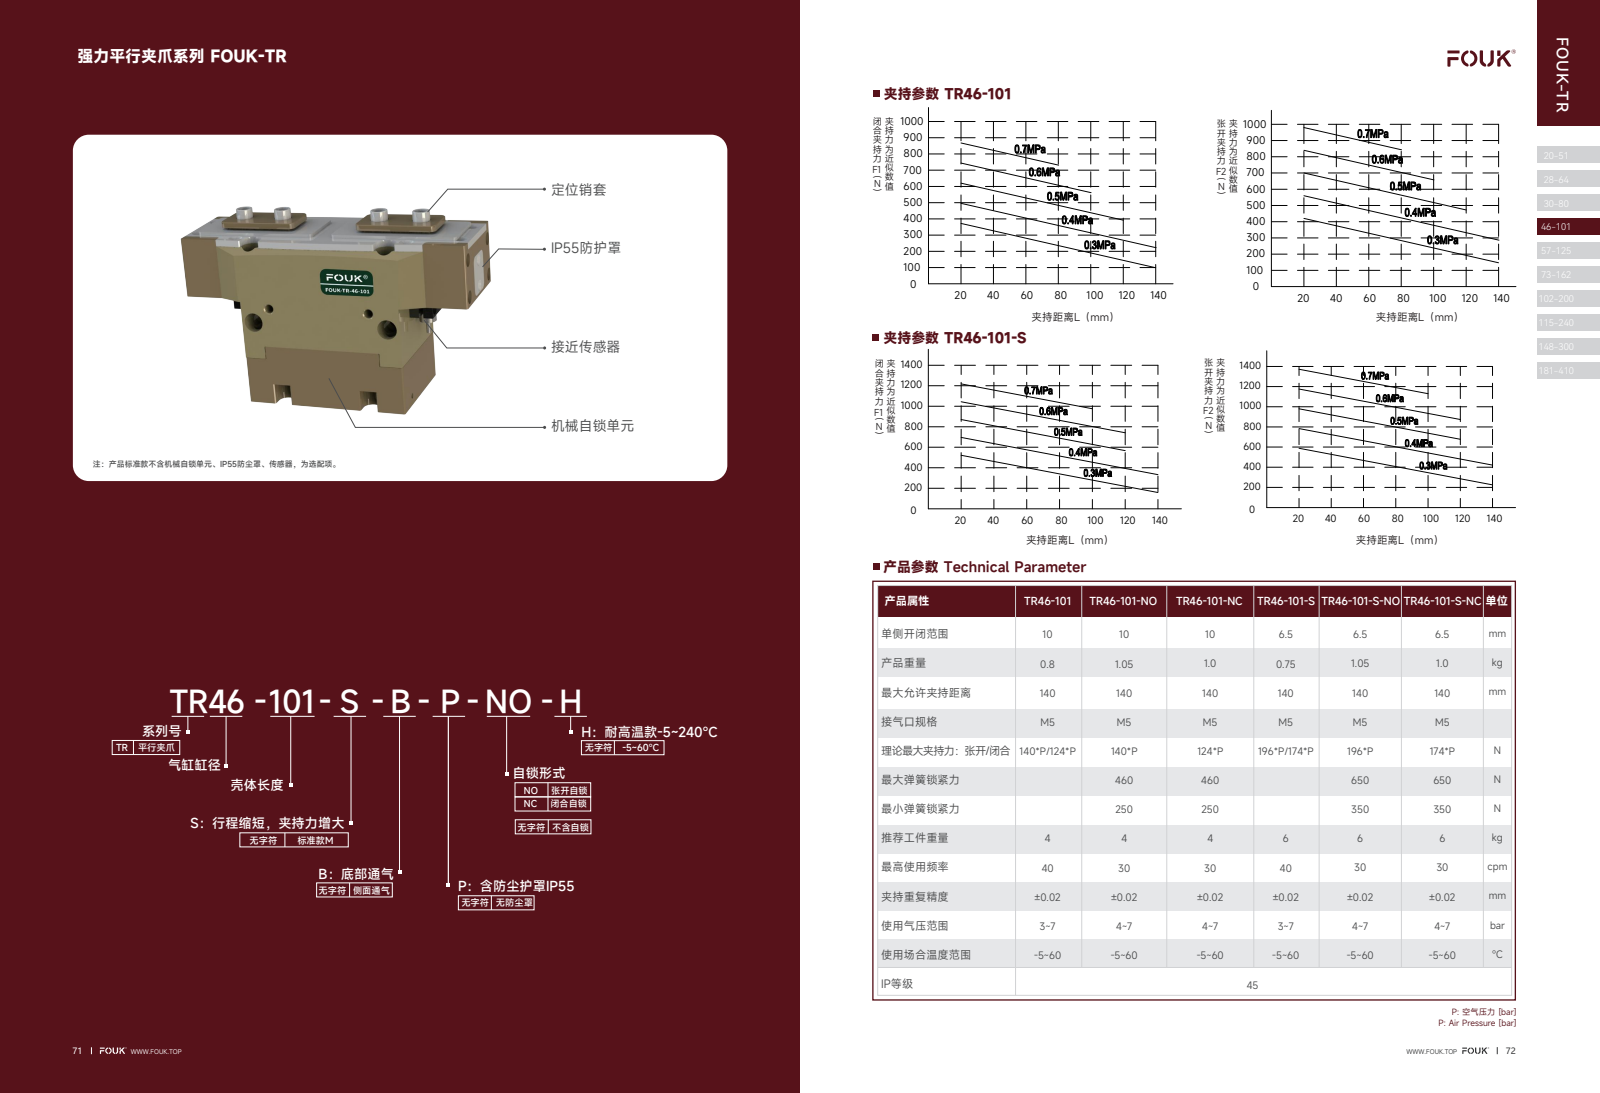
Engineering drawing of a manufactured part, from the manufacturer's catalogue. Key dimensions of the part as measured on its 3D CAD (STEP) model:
Part name (STEP PRODUCT): TR46-101-S; 25x12-R3
STEP written by: SolidWorks 2018 (CONFIG_CONTROL_DESIGN)
Units: millimetres
Bodies: 20 solids, 1207 faces (577 planar, 325 cylindrical, 305 other)
Overall size (bounding box): 111.24 × 61 × 50
Volume: 226 978 mm³ · Surface area: 65 480 mm²
Round holes (diameter × count): ⌀2.5 ×18, ⌀5 ×10, ⌀5.2 ×6, ⌀6 ×6, ⌀9.2 ×6, ⌀3.5 ×4, ⌀8 ×4, ⌀3 ×3, ⌀4.2 ×3, ⌀2 ×2, ⌀2.7 ×2, ⌀3.4 ×2
Round bosses / shafts (diameter × count): ⌀2 ×4, ⌀8 ×2, ⌀3.8 ×2, ⌀2.6 ×1, ⌀1.8 ×1
Partial cylindrical surfaces — rounded edges, fillets, slot ends (radius × count): R0.12 ×18, R0.12 ×12, R3 ×8, R5 ×8, R0.3 ×5, R0.2 ×4, R5.2 ×4, R0.15 ×2
Main face-to-face distances: 11.5, 19, 38.5, 47.8, 28.8, 50, 7, 27, 53.8, 34.8
Hole centre spacings: 17.18, 20, 24.7, 8.5, 34, 9.22, 17.13, 18.38
